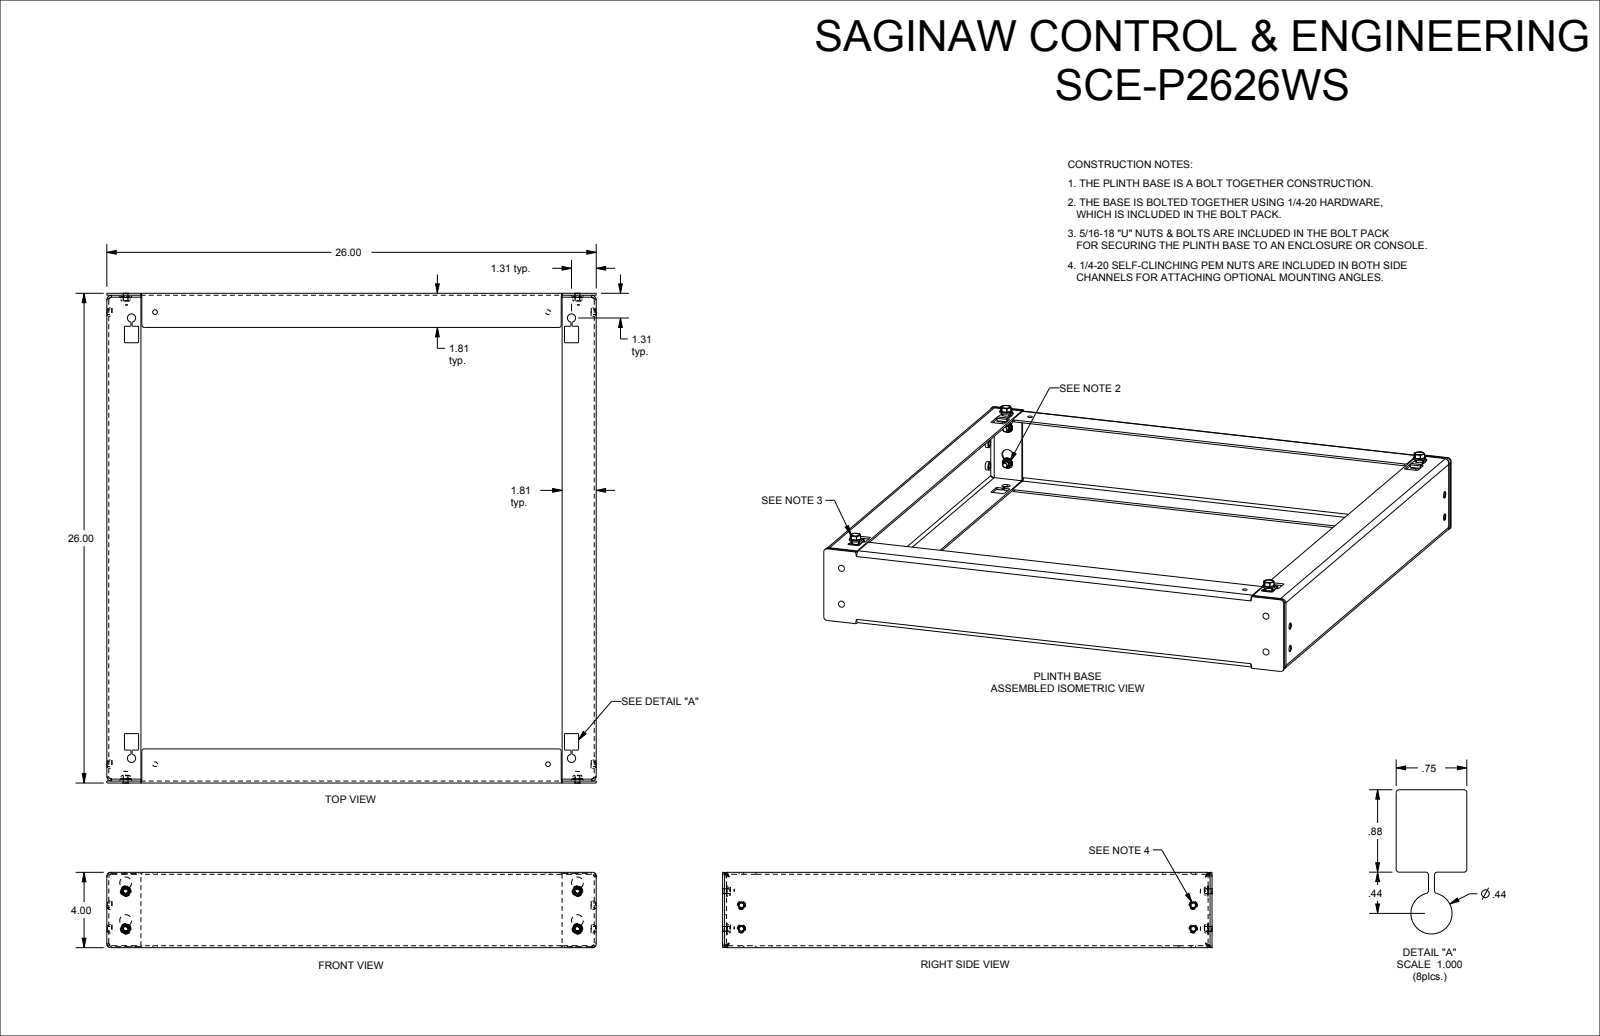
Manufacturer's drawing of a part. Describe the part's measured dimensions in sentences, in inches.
The part is named "SCE-P2626WS". Its 3-D file was written by "SolidWorks 2021 (AUTOMOTIVE_DESIGN)". It is 36 solids with 2626 faces: 870 planar, 364 cylindrical and 1392 other. Overall it measures 26.008 by 26 by 4.51 inches. Its volume is 78.4 cubic inches and its surface area 1 553 square inches. Round holes: 12 of diameter 0.25, 4 of diameter 0.25, 4 of diameter 0.32, 4 of diameter 0.344, 4 of diameter 0.437, 4 of diameter 0.625. Round bosses or shafts: 4 of diameter 0.563, 4 of diameter 0.44, 4 of diameter 0.37, 4 of diameter 0.343, 4 of diameter 0.337, 4 of diameter 0.31, 4 of diameter 0.248. Partial cylindrical surfaces (rounded edges, fillets, slot ends): 46 of radius 0.03, 24 of radius 0.01, 24 of radius 0.029, 8 of radius 0.132, 8 of radius 0.236, 8 of radius 0.5, 8 of radius 1, 6 of radius 0.06. The main face-to-face distances are 0.104, 25.896, 3.896, 25.792, 26, 4, 3.792, 1.813, 24.187, 1.709. The hole center spacings are 24, 0.44, 2, 23.375, 23.72, 24.004, 24.083, 1.25.
